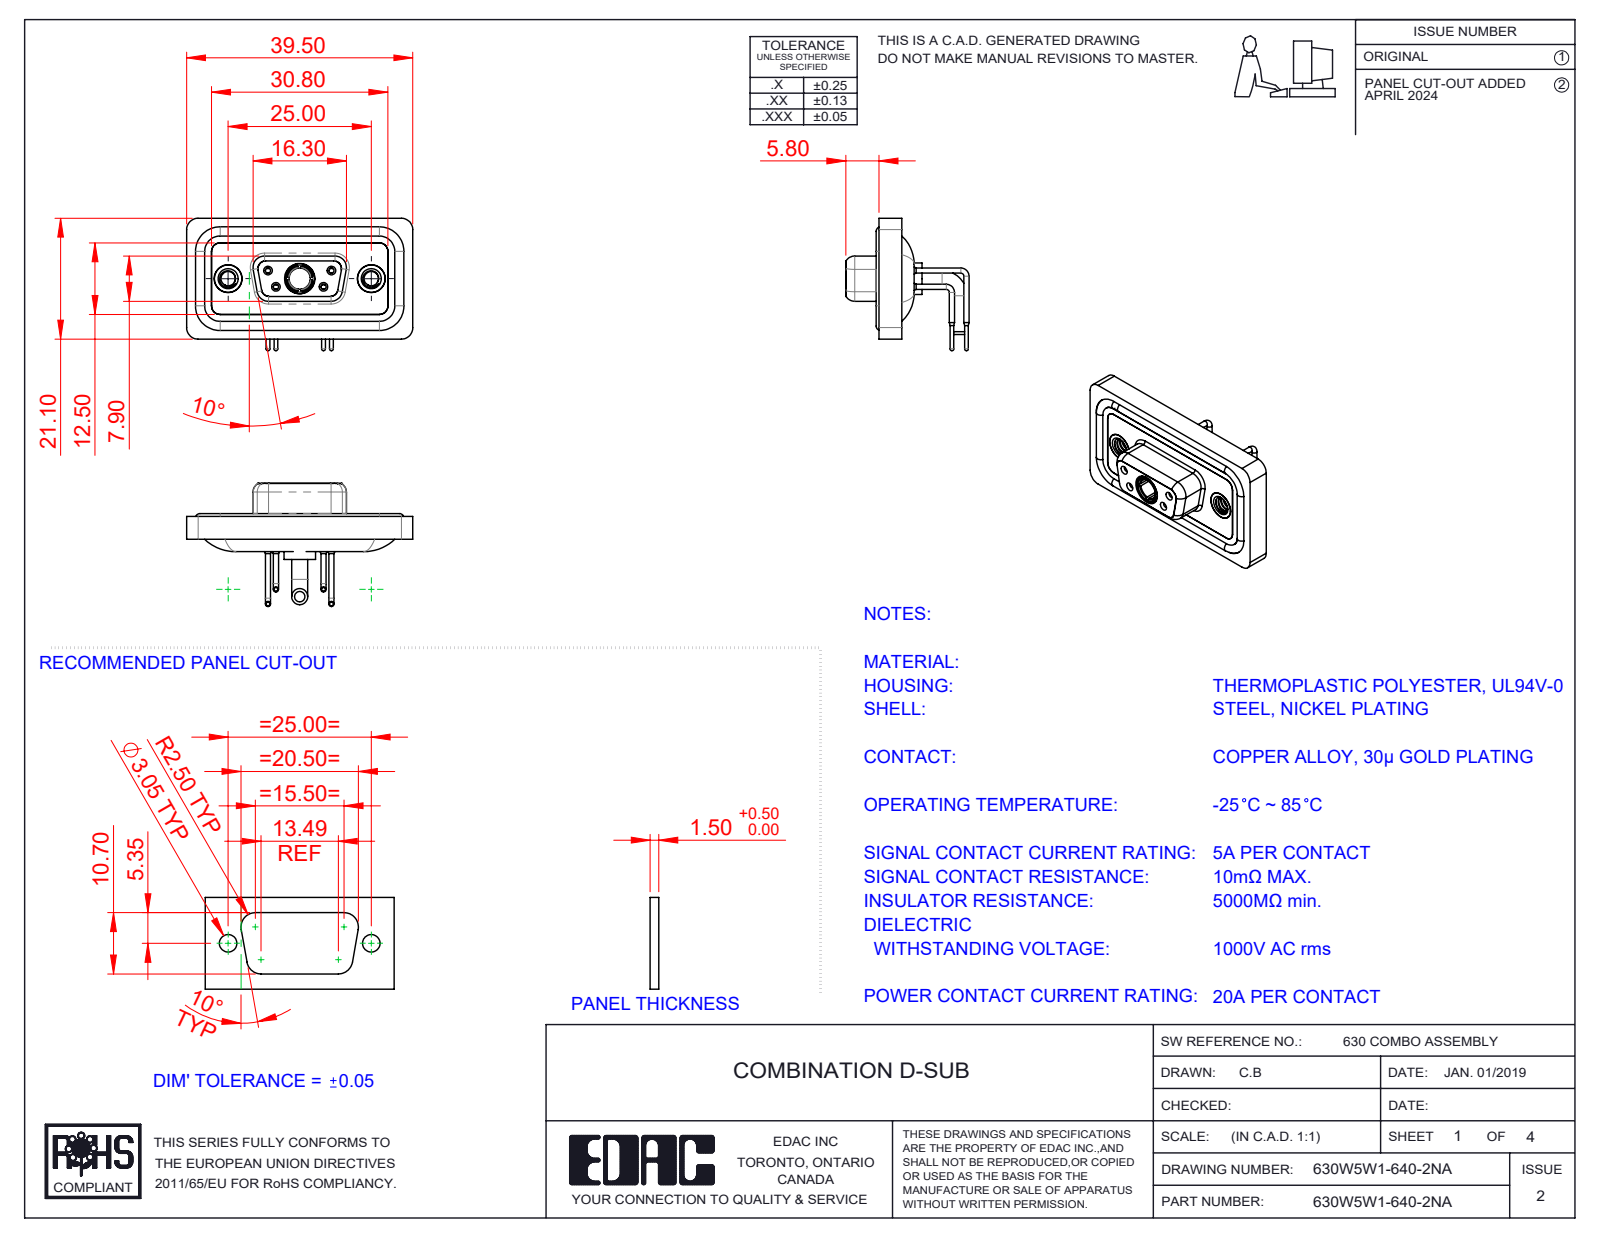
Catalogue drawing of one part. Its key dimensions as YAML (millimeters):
part_name: "630Combo Housing_5W1; 630W5W1-640-2NA; Power Socket_20A RA; 630Combo Contact Row 1_50 Contacts (+5 more)"
step_written_by: "SolidWorks 2023 (CONFIG_CONTROL_DESIGN)"
units: millimeters
bodies: {solids: 13, faces: 670, planar: 194, cylindrical: 303, other: 173}
overall_size: [39.5, 23.12, 21.53]
volume: 4821
surface_area: 7846
round_holes:
  - {diameter: 0.9, count: 4}
  - {diameter: 1.1, count: 4}
  - {diameter: 1.5, count: 4}
  - {diameter: 2, count: 4}
  - {diameter: 4.85, count: 3}
  - {diameter: 1.6, count: 2}
  - {diameter: 1.7, count: 2}
  - {diameter: 2.5, count: 2}
  - {diameter: 4, count: 2}
  - {diameter: 4.05, count: 2}
  - {diameter: 5, count: 2}
  - {diameter: 3.7, count: 1}
round_bosses_or_shafts:
  - {diameter: 1.6, count: 6}
  - {diameter: 0.9, count: 4}
  - {diameter: 0.65, count: 4}
  - {diameter: 4.95, count: 2}
  - {diameter: 4.8, count: 2}
  - {diameter: 2.8, count: 2}
  - {diameter: 5.5, count: 1}
  - {diameter: 5.2, count: 1}
partial_cylinders:
  - {radius: 1.5, count: 18}
  - {radius: 2, count: 18}
  - {radius: 1.35, count: 8}
  - {radius: 1.6, count: 8}
  - {radius: 0.25, count: 4}
  - {radius: 0.5, count: 4}
  - {radius: 0.6, count: 4}
  - {radius: 0.65, count: 4}
face_to_face_distances: [0.4, 1.8, 1.1, 2.9, 2.5, 1.6, 3.1, 2.1, 1.5, 0.5]
hole_center_spacings: [3.16, 5.72, 7.1, 12.5, 18.1, 4.39, 4.4, 8.31]
